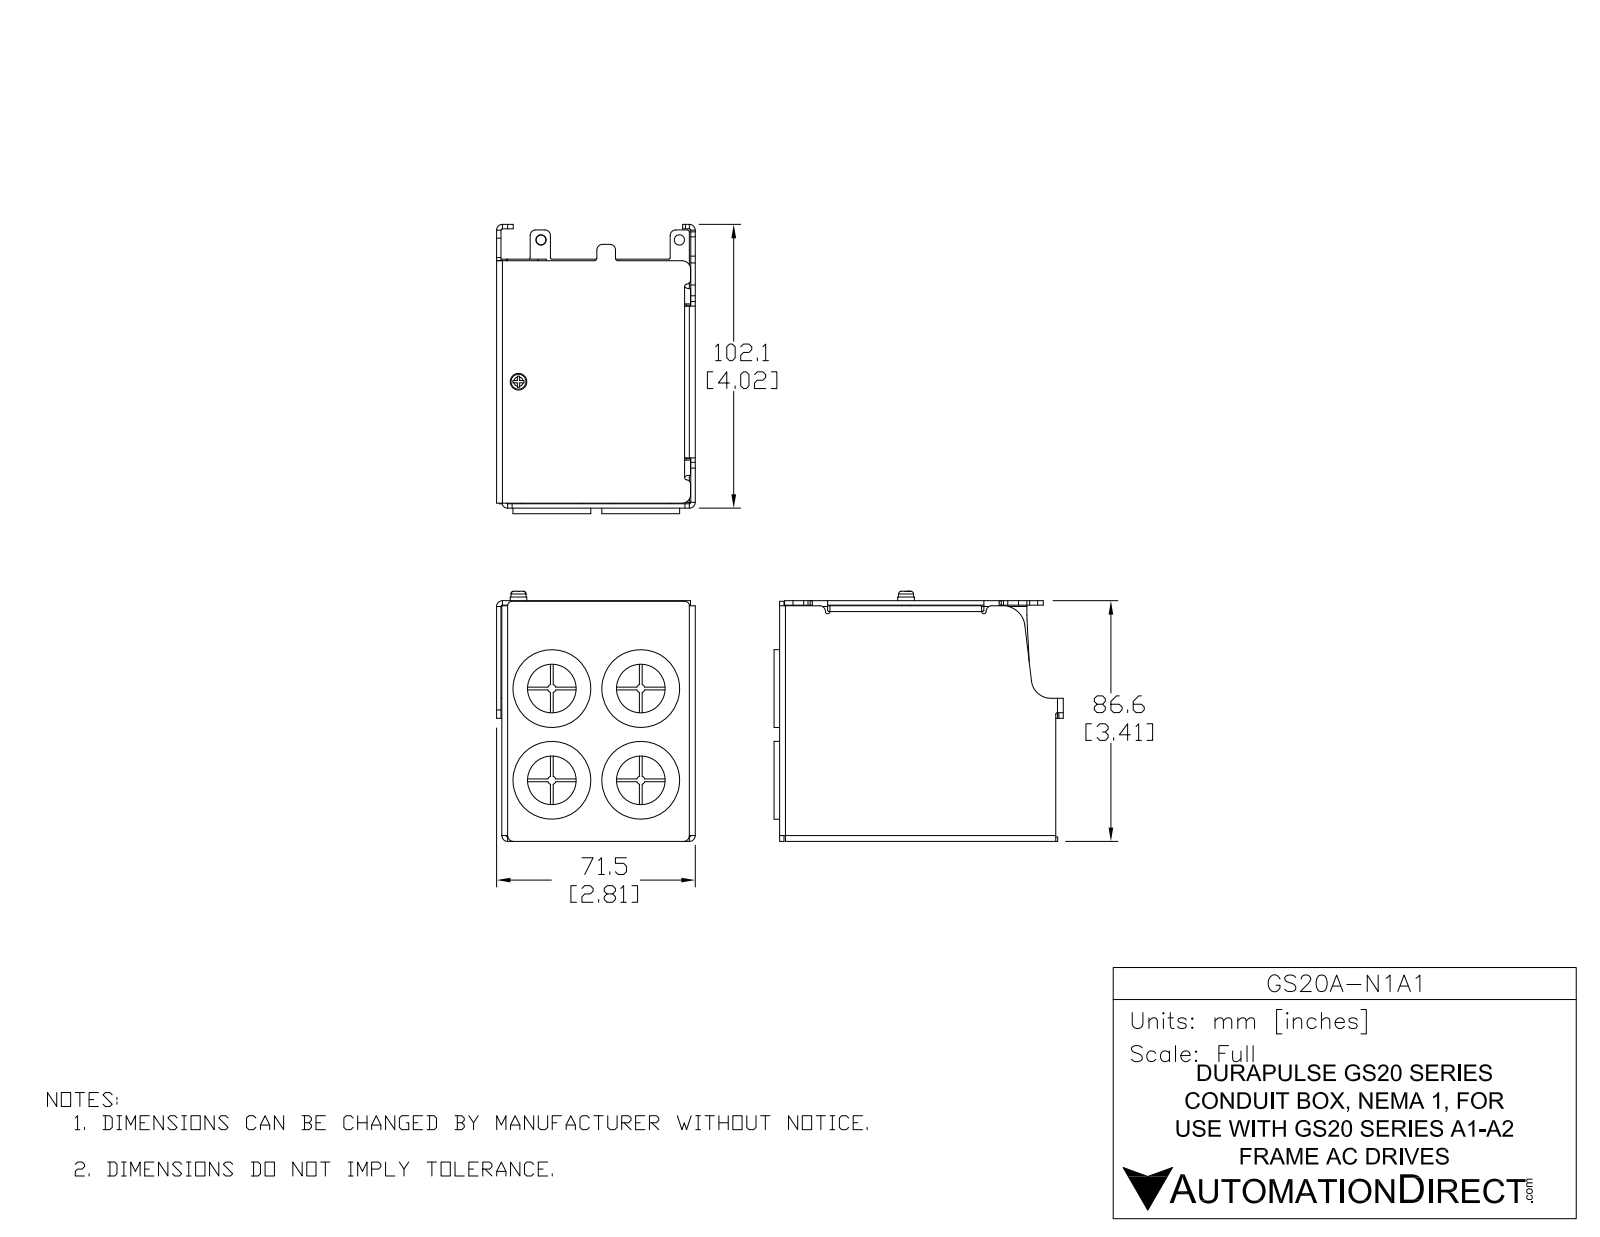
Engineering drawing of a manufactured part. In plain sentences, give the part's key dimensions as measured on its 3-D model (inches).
The part is named "GS20A-N1A1". Its 3-D file was written by "SolidWorks 2017 (AUTOMOTIVE_DESIGN)". It is 12 solids with 459 faces: 221 planar, 188 cylindrical and 50 other. Overall it measures 4.098 by 3.602 by 2.815 inches. Its volume is 4.038 cubic inches and its surface area 134 square inches. Round holes: 4 of diameter 0.689, 4 of diameter 0.886, 2 of diameter 0.116, 2 of diameter 0.138, 2 of diameter 0.146, 1 of diameter 0.097, 1 of diameter 0.118, 1 of diameter 0.157. Round bosses or shafts: 4 of diameter 1.102, 4 of diameter 0.846, 3 of diameter 0.193, 3 of diameter 0.166, 2 of diameter 0.276, 2 of diameter 0.252, 2 of diameter 0.24, 2 of diameter 0.118. Partial cylindrical surfaces (rounded edges, fillets, slot ends): 19 of radius 0.02, 18 of radius 0.083, 9 of radius 0.118, 7 of radius 0.031, 7 of radius 0.059, 7 of radius 0.079, 4 of radius 0.012, 4 of radius 0.039. The main face-to-face distances are 0.063, 2.677, 3.346, 0.075, 2.752, 2.74, 2.614, 3.283, 3.409, 2.689. The hole center spacings are 1.26, 1.299, 1.81, 0.689, 0.79, 1.357, 1.575, 1.719.
